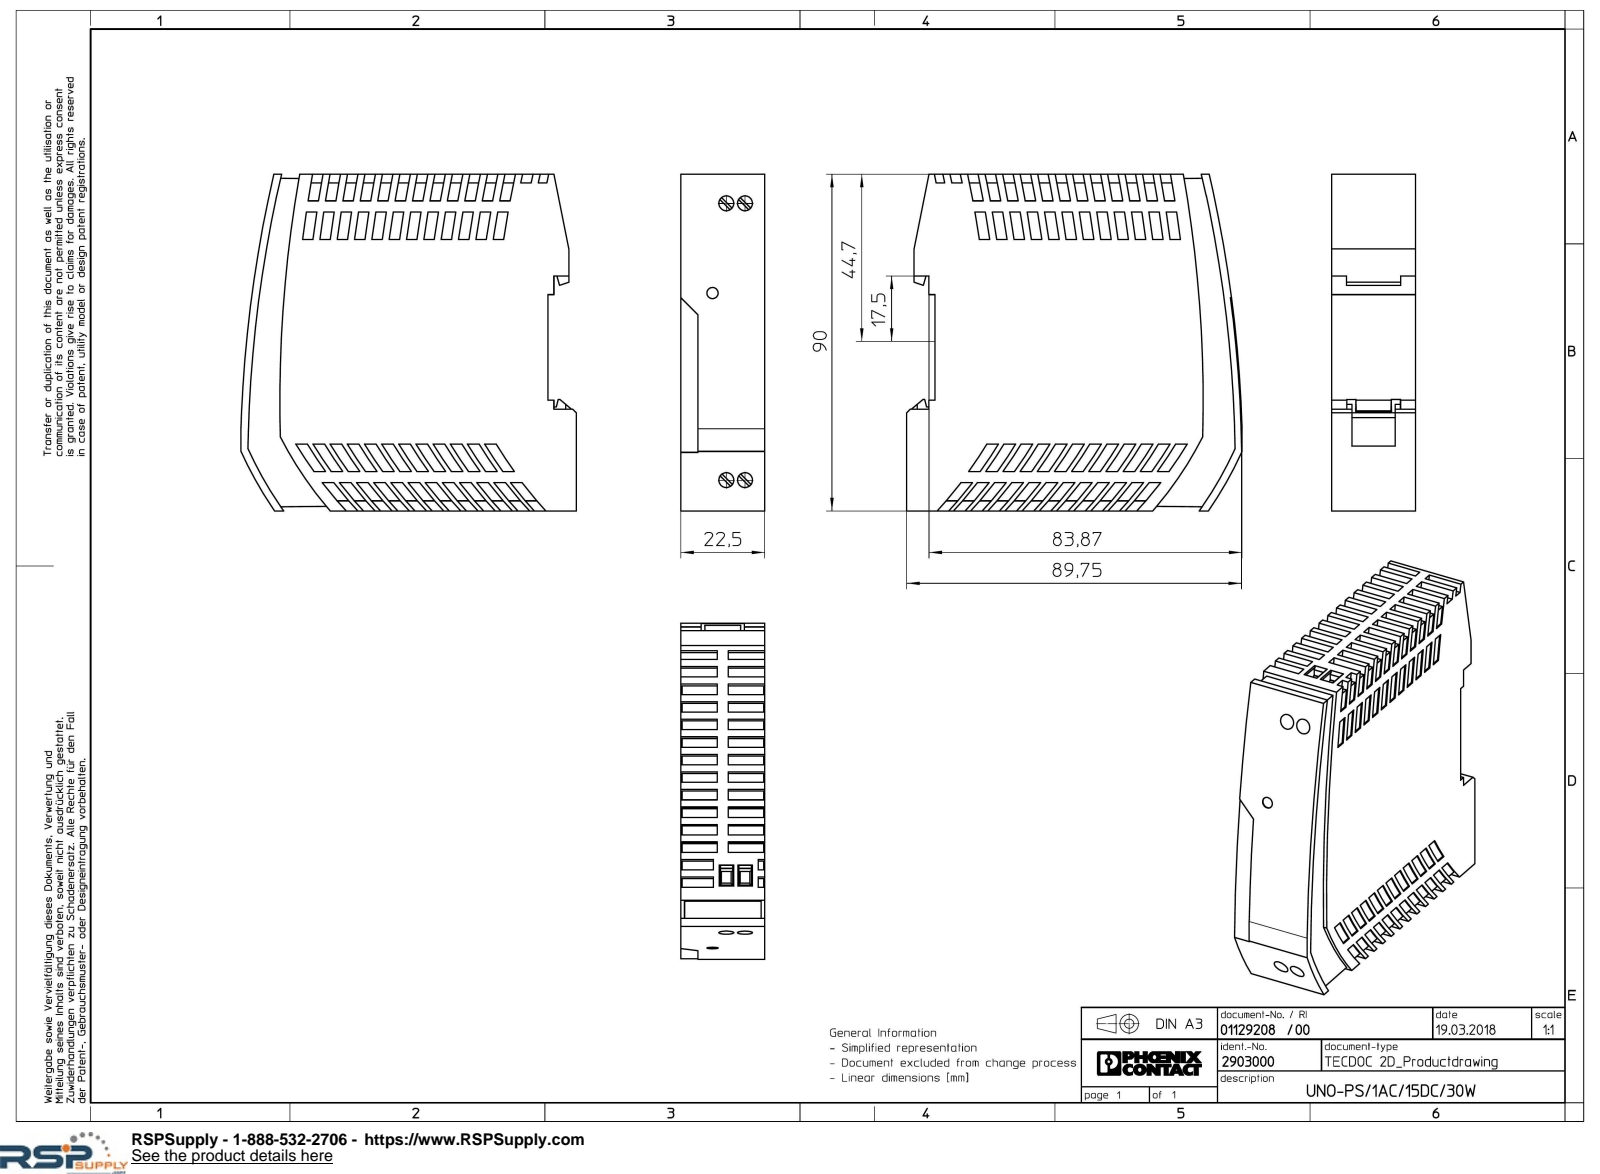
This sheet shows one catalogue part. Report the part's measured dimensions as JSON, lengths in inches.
{"part_name": "UNO_PS_1AC_15DC_30W-select", "step_written_by": "Creo Elements/Direct Modeling 18.1I 14-Aug-2016 (C) Parametric Technology GmbH (AUTOMOTIVE_DESIGN)", "units": "inches", "bodies": {"solids": 1, "faces": 728, "planar": 511, "cylindrical": 215, "other": 2}, "overall_size": [3.543, 3.538, 0.886], "volume_in3": 9.824, "surface_area_in2": 42.33, "round_holes": [[0.157, 4]], "partial_cylinders_radius": [[4.37, 26], [3.858, 1], [3.88, 1], [3.937, 1], [11.128, 1], [11.217, 1], [11.29, 1], [11.471, 1]], "face_to_face_distances": [0.886, 0.874, 0.039, 0.028, 0.846, 0.835, 0.862, 3.543, 0.106, 3.437], "hole_center_spacings": [0.197, 2.913, 2.92]}
